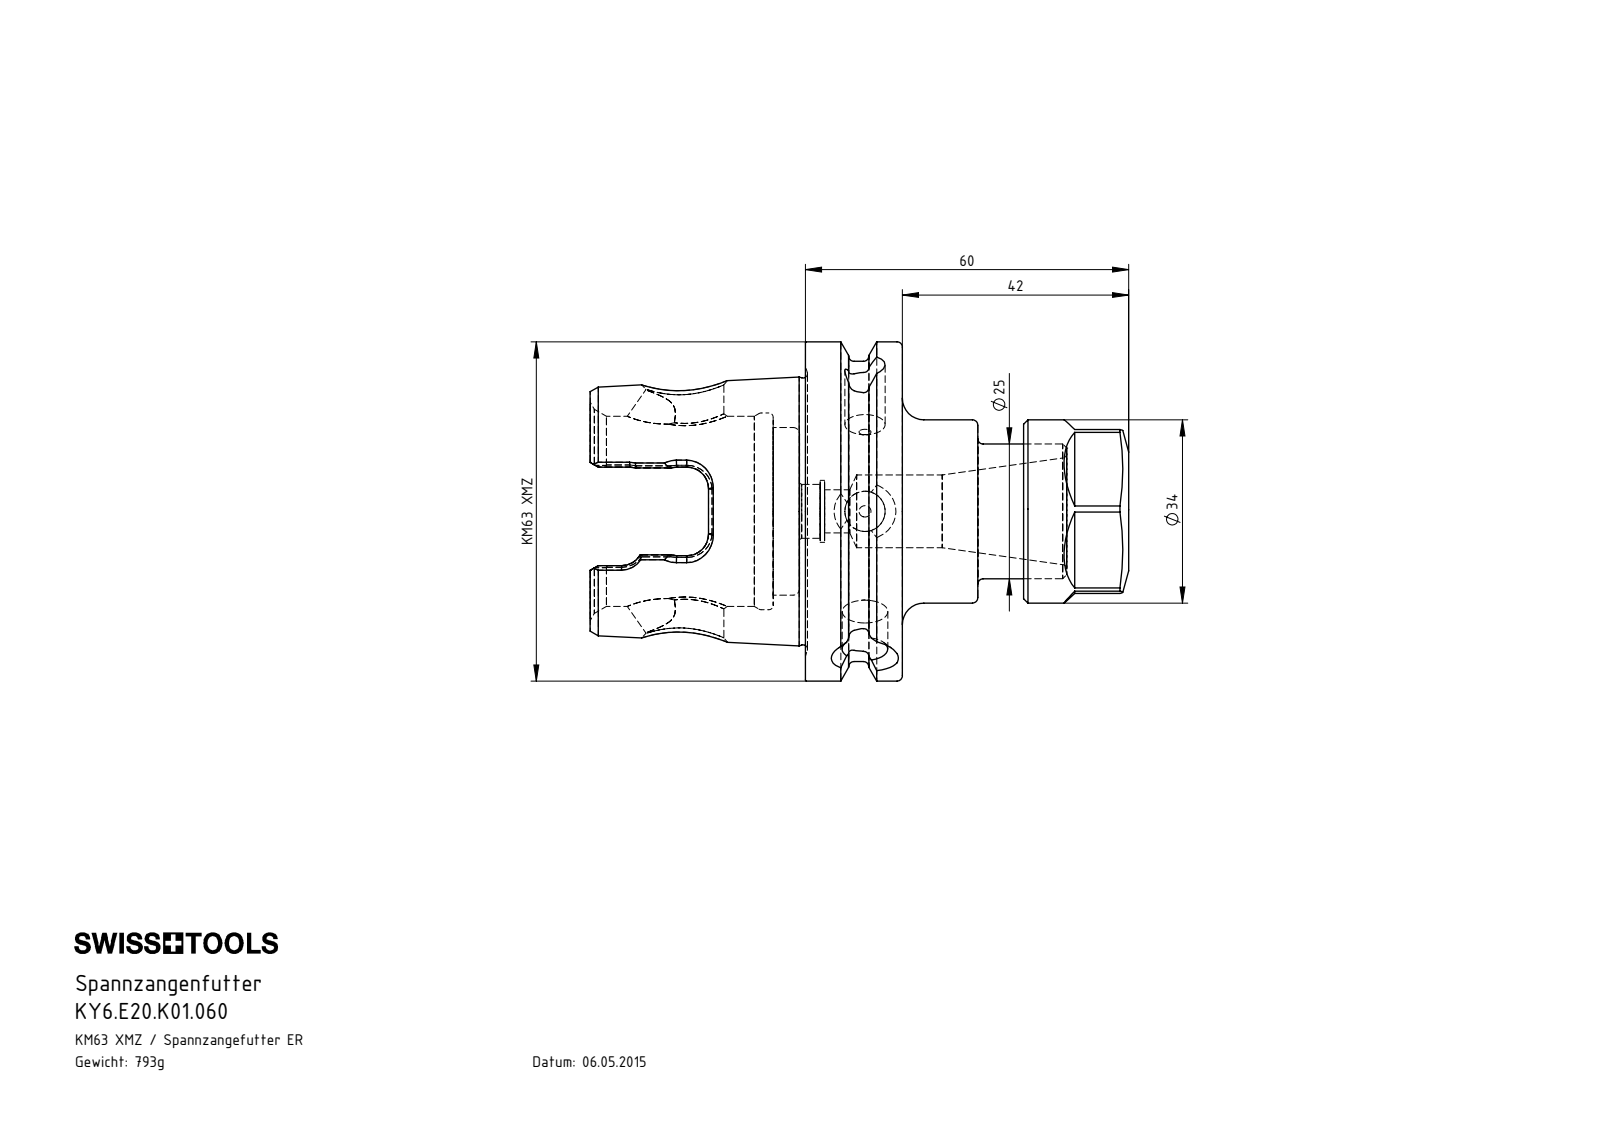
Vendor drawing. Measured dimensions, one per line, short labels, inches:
name: KY6.E20.K01.060; E20-ER2.001.020; KY6-E20.K01.060_B
written by: SolidWorks 2017 (CONFIG_CONTROL_DESIGN)
unit: in
bodies: 2 solids, 269 faces (64 planar, 66 cylindrical, 139 other)
size: 3.935 × 2.478 × 2.478
volume: 6.164 in³; area: 44.32 in²
holes: 2× ⌀0.294, 1× ⌀0.315, 1× ⌀0.334, 1× ⌀0.394, 1× ⌀0.453, 1× ⌀0.531, 1× ⌀0.571, 1× ⌀0.626, 1× ⌀0.925, 1× ⌀1.004, 1× ⌀1.224, 1× ⌀1.389
bosses: 1× ⌀2.478, 1× ⌀2.193, 1× ⌀1.339, 1× ⌀0.984
rounds: 6× R0.157, 2× R0.277, 2× R0.378
face distances: 0.709, 0.043, 0.752, 1.638, 1.594, 0.886, 1.181, 1.303, 1.26, 0.551
